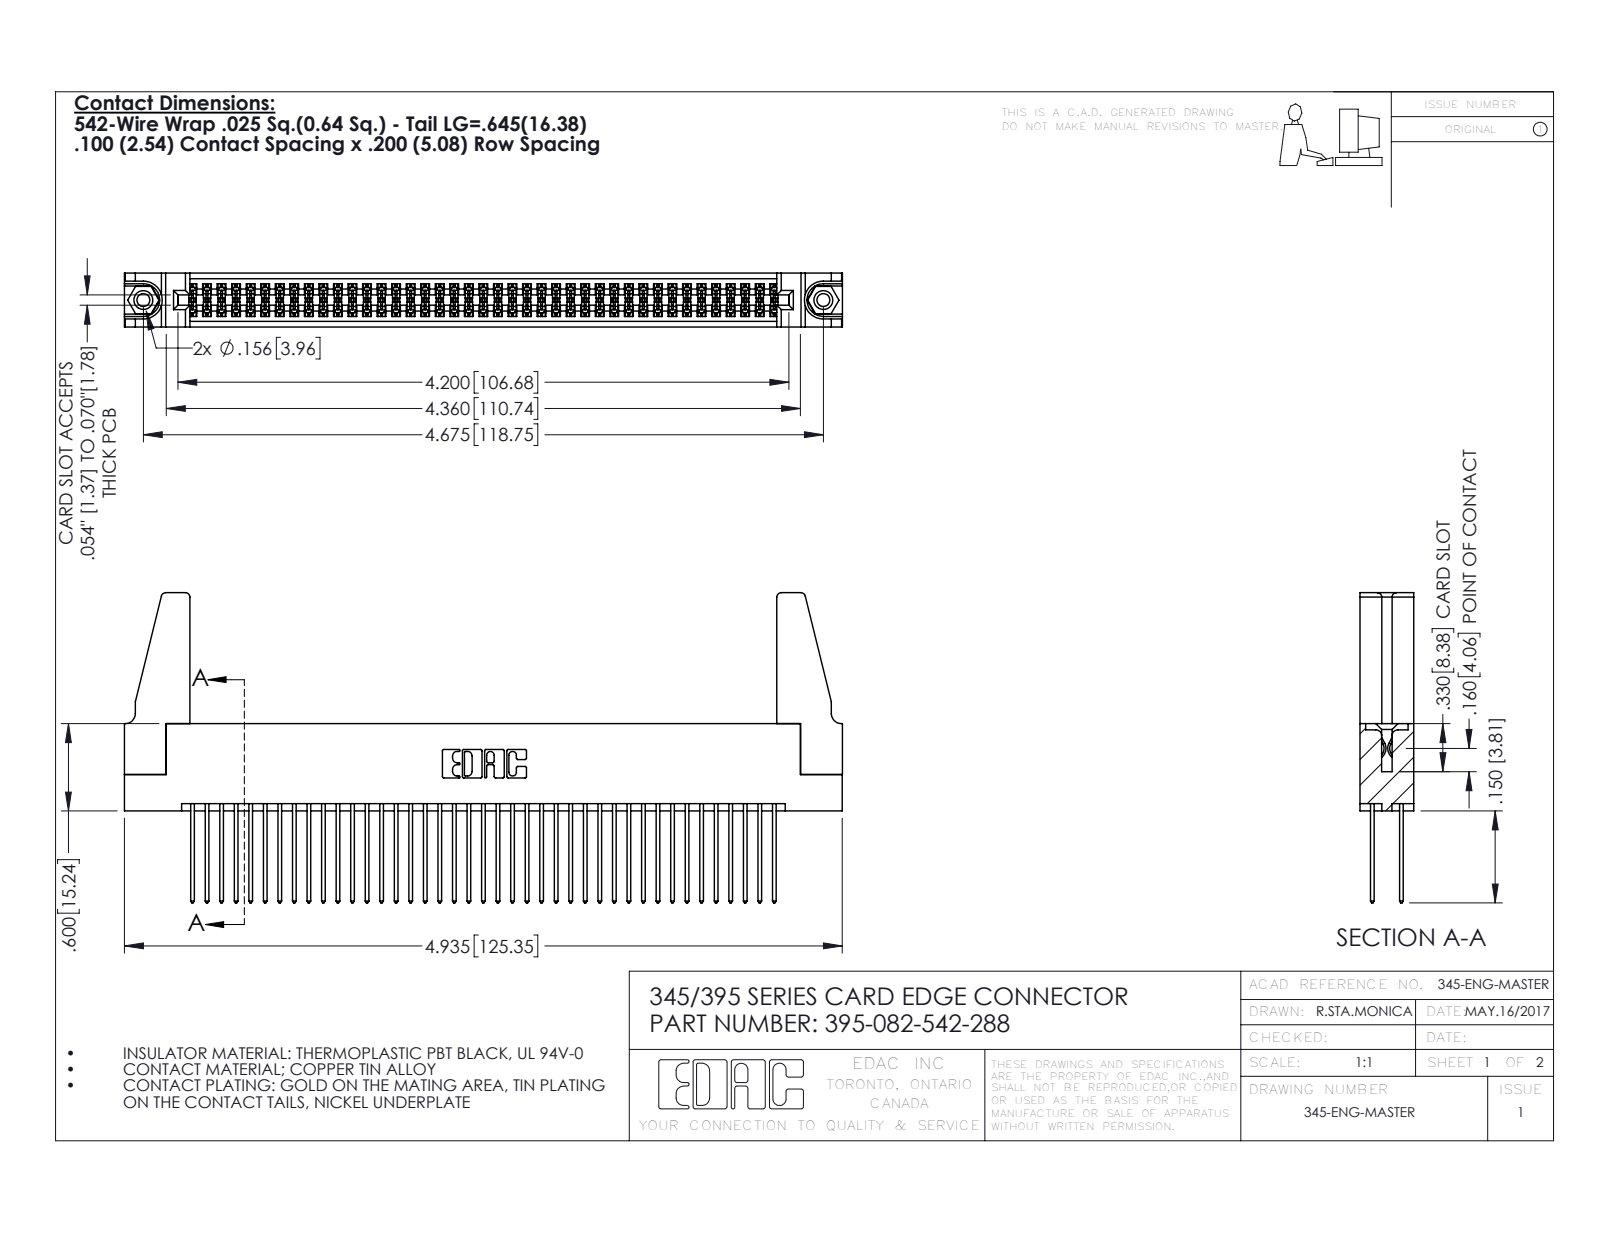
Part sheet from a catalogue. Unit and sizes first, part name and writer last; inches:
Units: inches
Overall size (bounding box): 4.936 × 2.132 × 0.37
Round holes (diameter × count): ⌀0.089 ×2, ⌀0.125 ×2, ⌀0.156 ×2, ⌀0.064 ×1
Round bosses / shafts (diameter × count): ⌀0.155 ×2
Partial cylindrical surfaces — rounded edges, fillets, slot ends (radius × count): R0.006 ×123, R0.01 ×82, R0.01 ×22, R0.03 ×8, R0.007 ×6, R0.031 ×6, R0.026 ×3, R0.014 ×2
Main face-to-face distances: 0.072, 0.298, 0.2, 0.098, 0.272, 0.025, 0.37, 0.225, 0.175, 0.149
Hole centre spacings: 0.27, 4.439, 4.675
Volume: 0.964 in³ · Surface area: 36.34 in²
Bodies: 87 solids, 4350 faces (2858 planar, 1476 cylindrical, 16 other)
Part name (STEP PRODUCT): 345 Part_Flush Mounting Lugs - 0.156 Dia-TH; 395-082-542-288; 345-292-001_345-293-142; 345-220-078_345-220-088 (+1 more)
STEP written by: SolidWorks 2016 (CONFIG_CONTROL_DESIGN)
